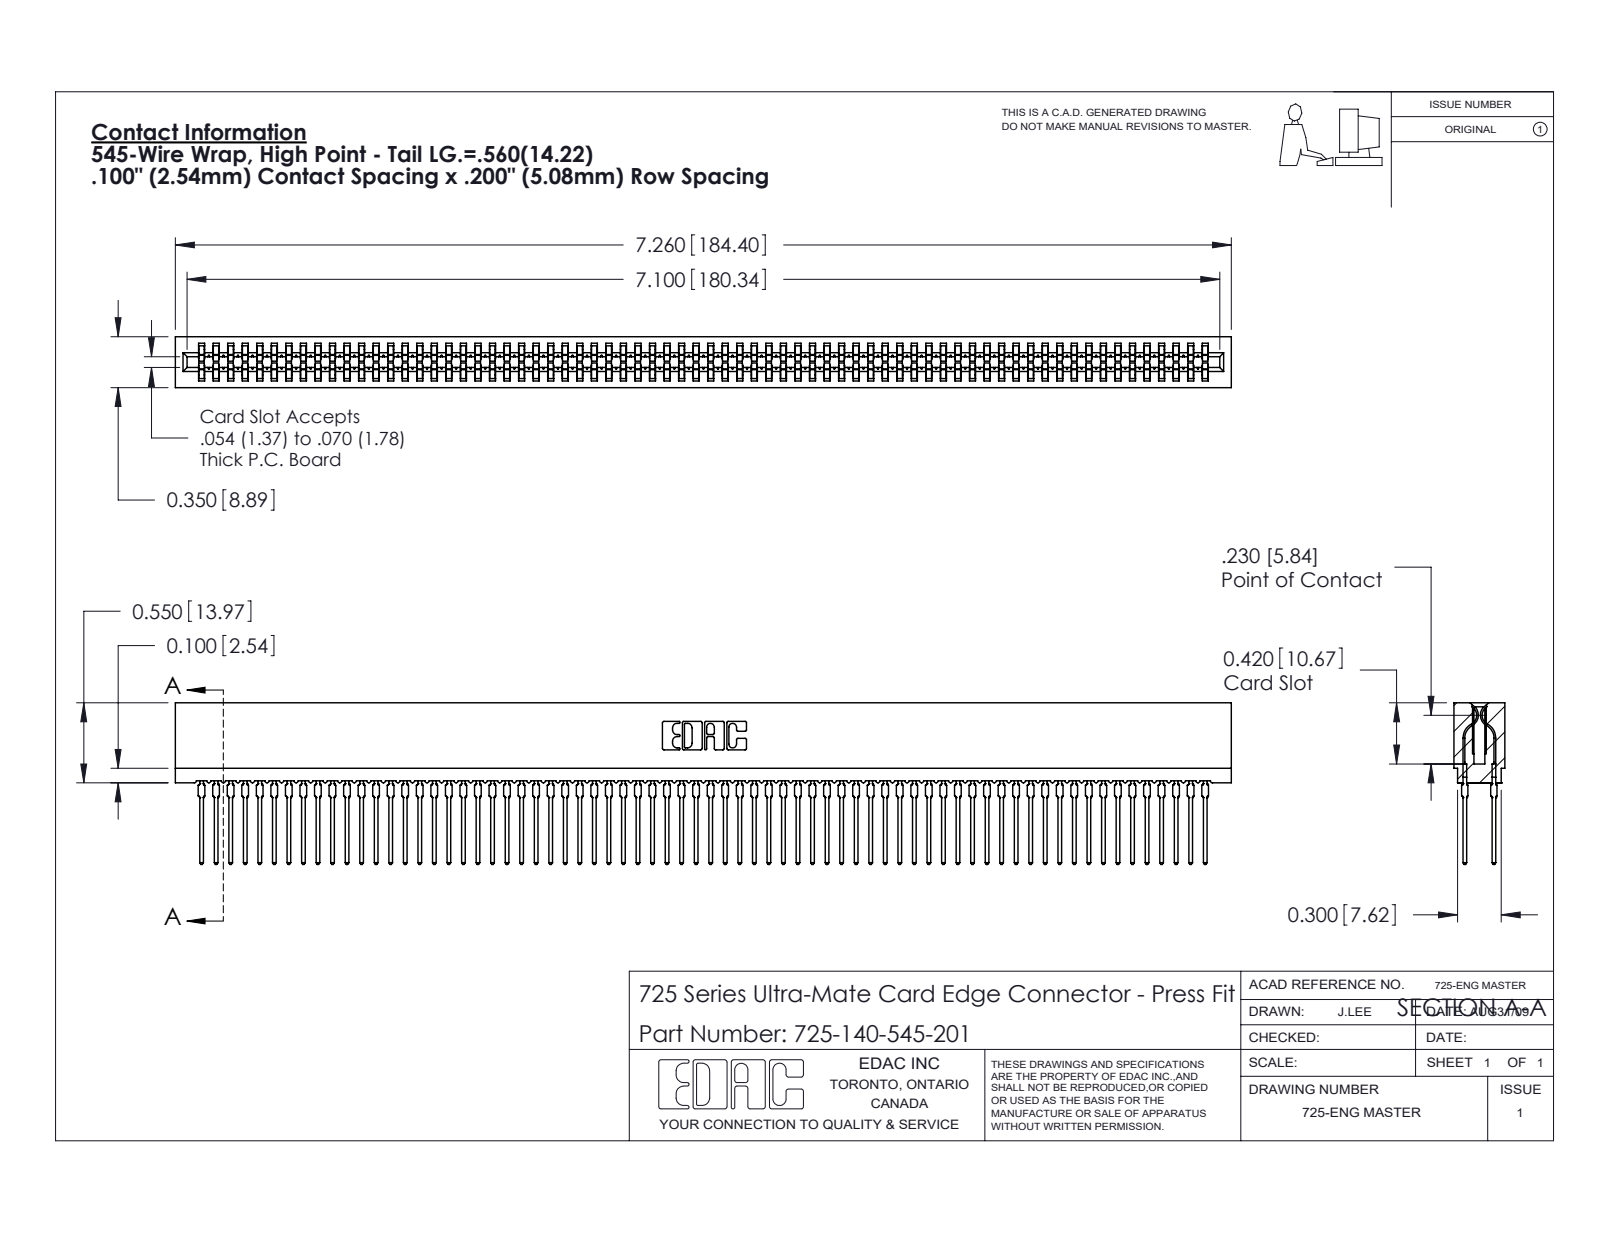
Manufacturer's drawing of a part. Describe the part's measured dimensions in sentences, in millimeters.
The part is named "745-292-001_545; 725 Part_Insulator Option - 01; 725-140-545-201". Its 3-D file was written by "SolidWorks 2020 (CONFIG_CONTROL_DESIGN)". It is 141 solids with 12625 faces: 6495 planar, 2490 cylindrical and 3640 other. Overall it measures 184.4 by 28.2 by 8.9 millimeters. Its volume is 15 000 cubic millimeters and its surface area 34 370 square millimeters. Partial cylindrical surfaces (rounded edges, fillets, slot ends): 280 of radius 0.5, 140 of radius 0.4, 22 of radius 0.3, 8 of radius 0.1, 8 of radius 0.3, 6 of radius 0.2, 6 of radius 0.8, 3 of radius 0.7. The main face-to-face distances are 1.6, 7.3, 5.1, 8.9, 5.4, 3.5, 1.9, 3.8, 2.2, 6.7.
